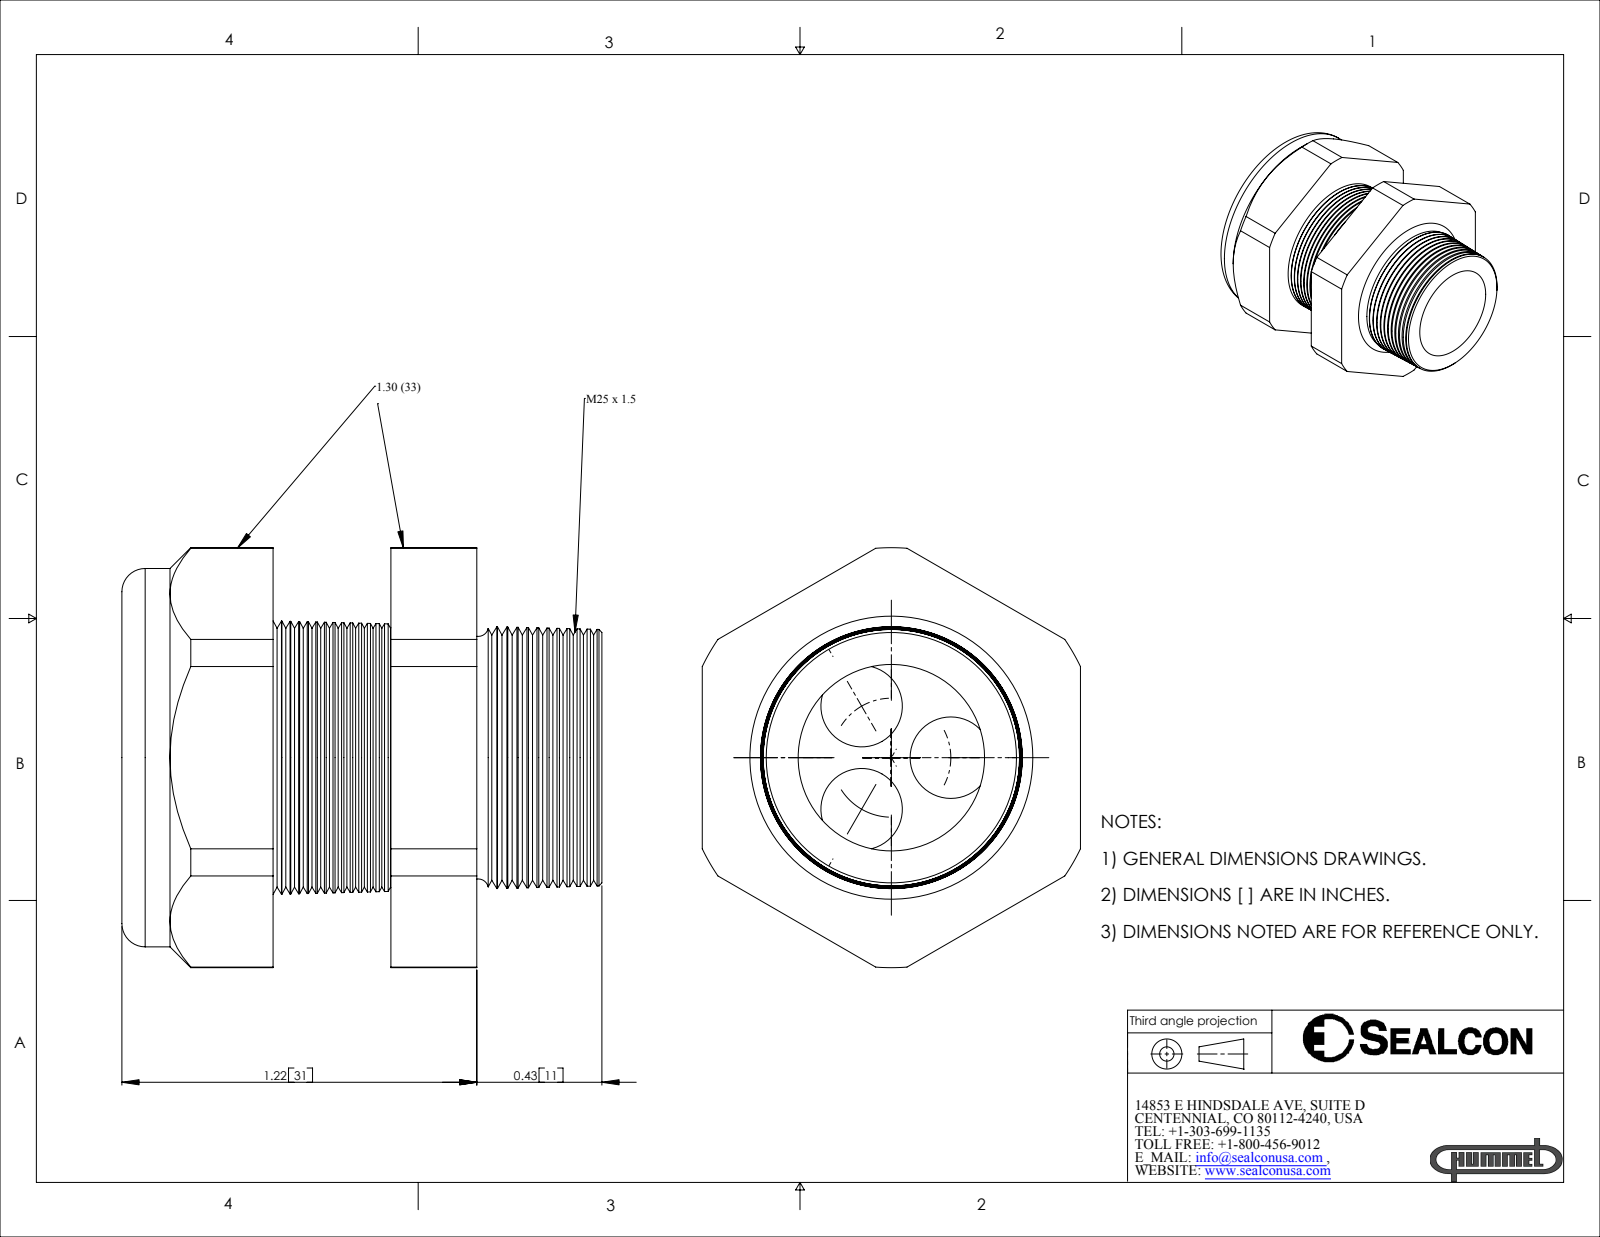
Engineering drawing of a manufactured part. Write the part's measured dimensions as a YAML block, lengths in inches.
part_name: "CD25M2-GY"
step_written_by: "SolidWorks 2007 (CONFIG_CONTROL_DESIGN)"
units: inches
bodies: {solids: 2, faces: 212, planar: 20, cylindrical: 26, other: 166}
overall_size: [1.65, 1.443, 1.3]
volume: 1.13
surface_area: 17.06
round_holes:
  - {diameter: 0.28, count: 3}
  - {diameter: 0.69, count: 1}
  - {diameter: 0.71, count: 1}
round_bosses_or_shafts:
  - {diameter: 1.3, count: 1}
partial_cylinders:
  - {radius: 0.721, count: 1}
face_to_face_distances: [1.3, 0.405, 0.7, 0.295, 0.52, 0.925, 1.22, 1.65, 1.13, 0.725]
hole_center_spacings: [0.354, 0.205, 0.204]
